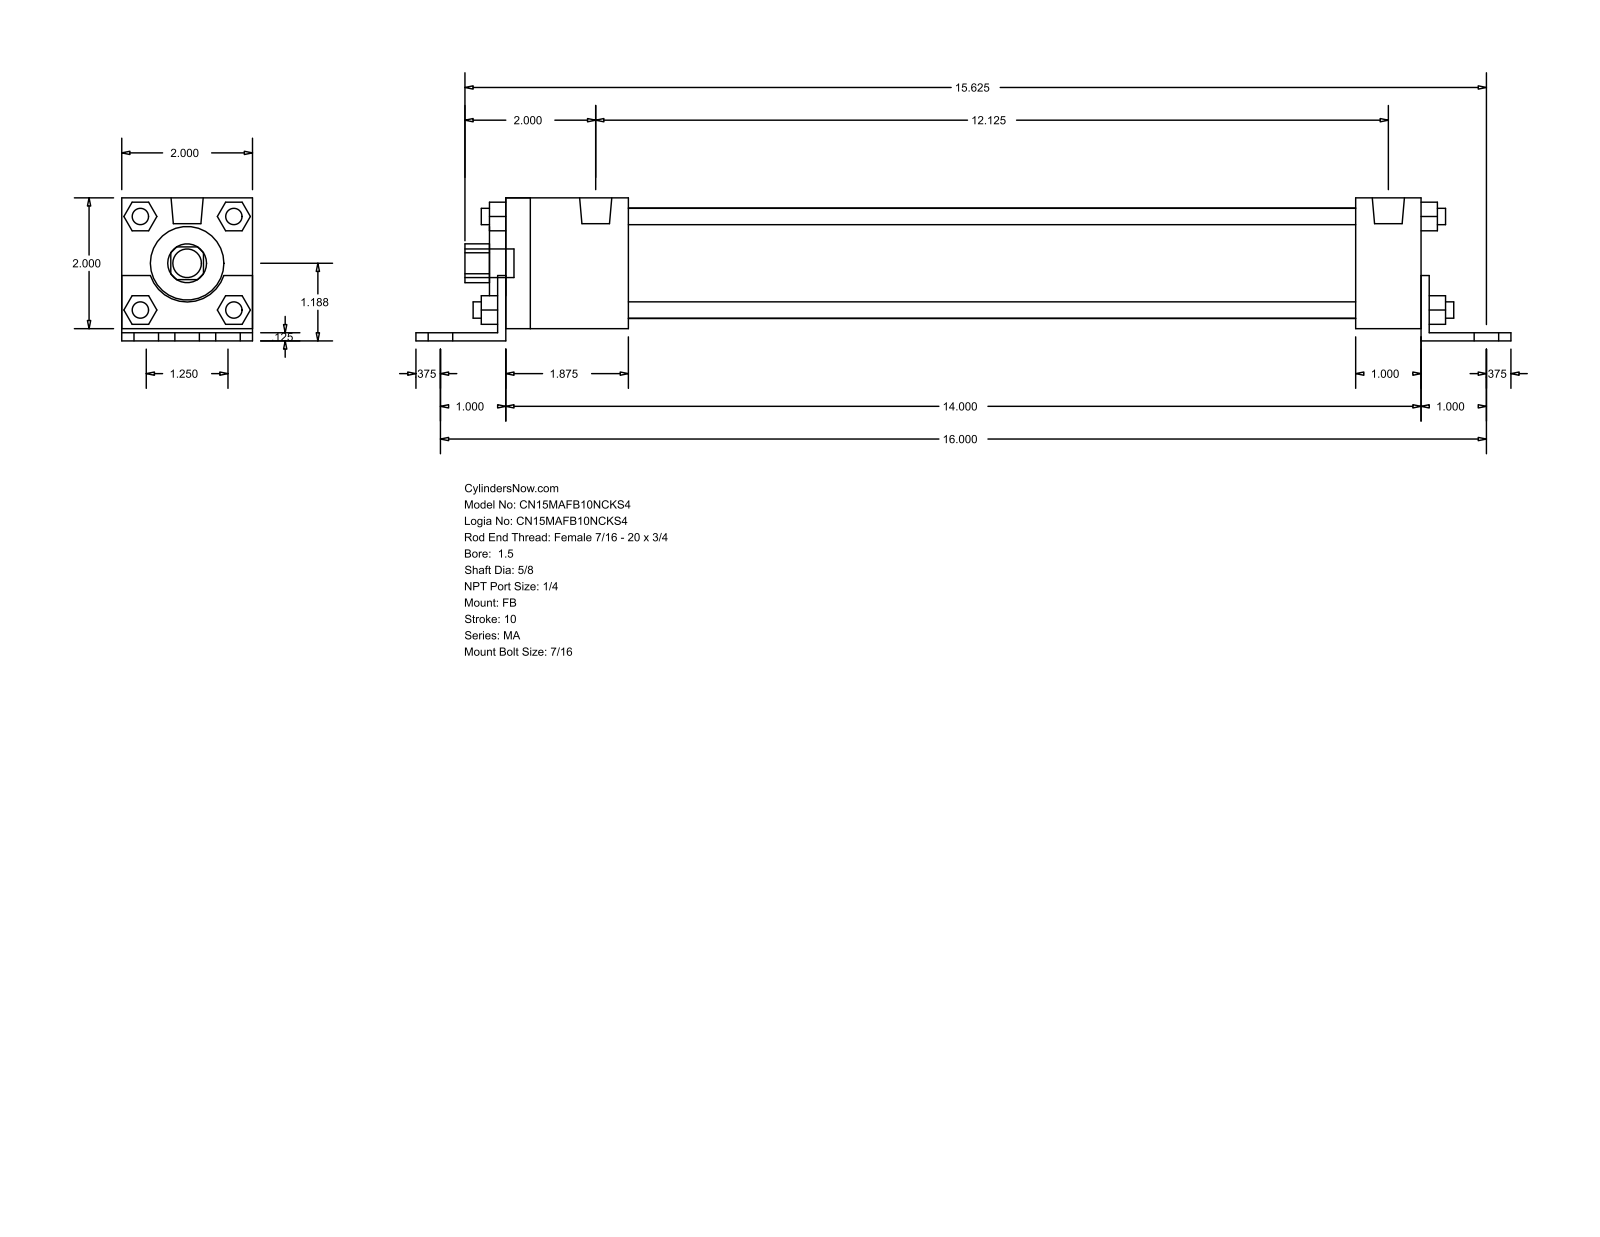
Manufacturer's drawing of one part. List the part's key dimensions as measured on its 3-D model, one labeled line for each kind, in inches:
Part name (STEP PRODUCT): MA_FB__0150_0.625
STEP written by: GSSL Pune (CONFIG_CONTROL_DESIGN)
Units: inches
Bodies: 0 solids, 140 faces (105 planar, 35 cylindrical, 0 other)
Overall size (bounding box): 16.75 × 2.187 × 2
Round holes (diameter × count): ⌀0.625 ×1, ⌀1.125 ×1, ⌀1.69 ×1
Round bosses / shafts (diameter × count): ⌀0.437 ×7, ⌀0.313 ×4, ⌀0.25 ×4, ⌀0.492 ×2
Partial cylindrical surfaces — rounded edges, fillets, slot ends (radius × count): R0.297 ×1, R0.593 ×1
Main face-to-face distances: 2, 0.125, 0.187, 2.187, 0.063, 2.063, 14.25, 0.125, 14, 1.125
